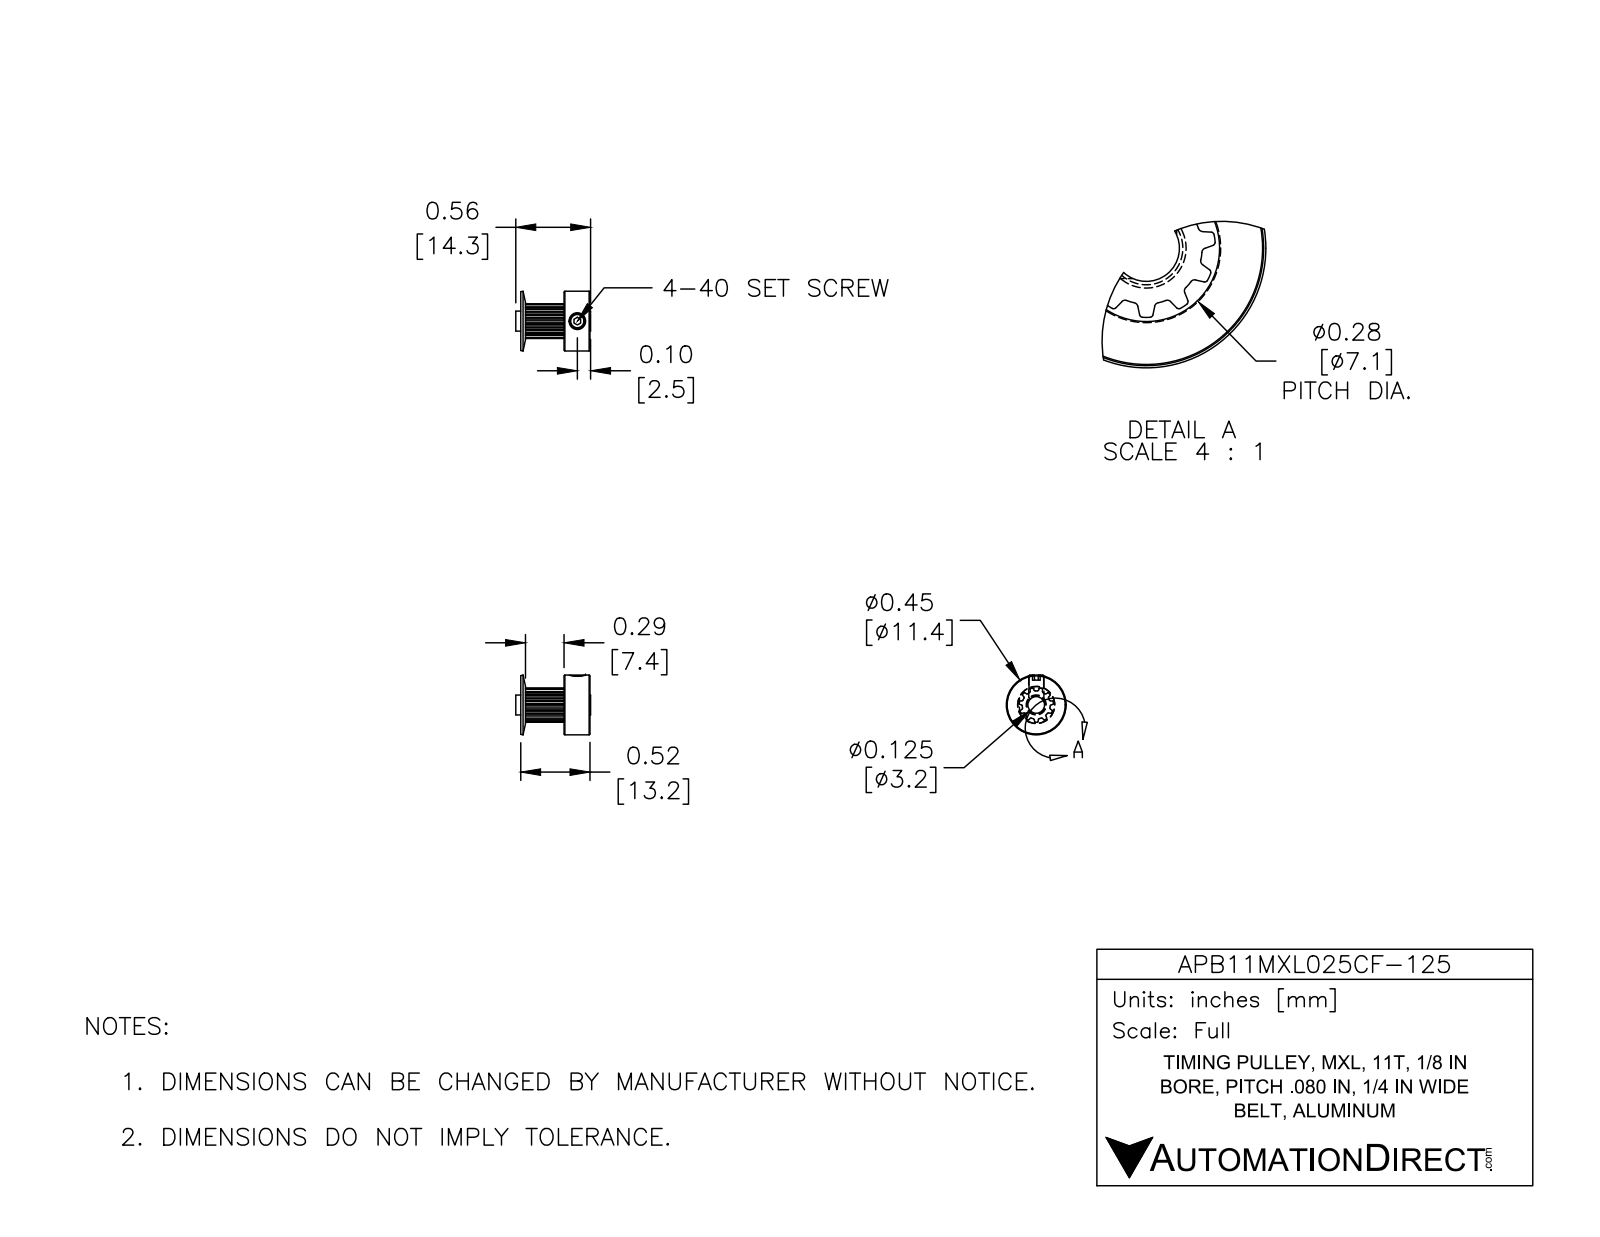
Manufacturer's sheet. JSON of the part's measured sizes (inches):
{"part_name": "APB11MXL025CF-125", "step_written_by": "SolidWorks 2016 (AUTOMOTIVE_DESIGN)", "units": "inches", "bodies": {"solids": 2, "faces": 142, "planar": 37, "cylindrical": 87, "other": 18}, "overall_size": [0.563, 0.45, 0.45], "volume_in3": 0.039, "surface_area_in2": 1.467, "round_holes": [[0.114, 1], [0.125, 1]], "round_bosses_or_shafts": [[0.45, 1], [0.15, 1], [0.11, 1]], "partial_cylinders_radius": [[0.005, 22], [0.009, 22], [0.105, 1], [0.13, 1]], "face_to_face_distances": [0.194, 0.309, 0.504, 0.019, 0.29, 0.485, 0.098, 0.05, 0.508, 0.489]}
